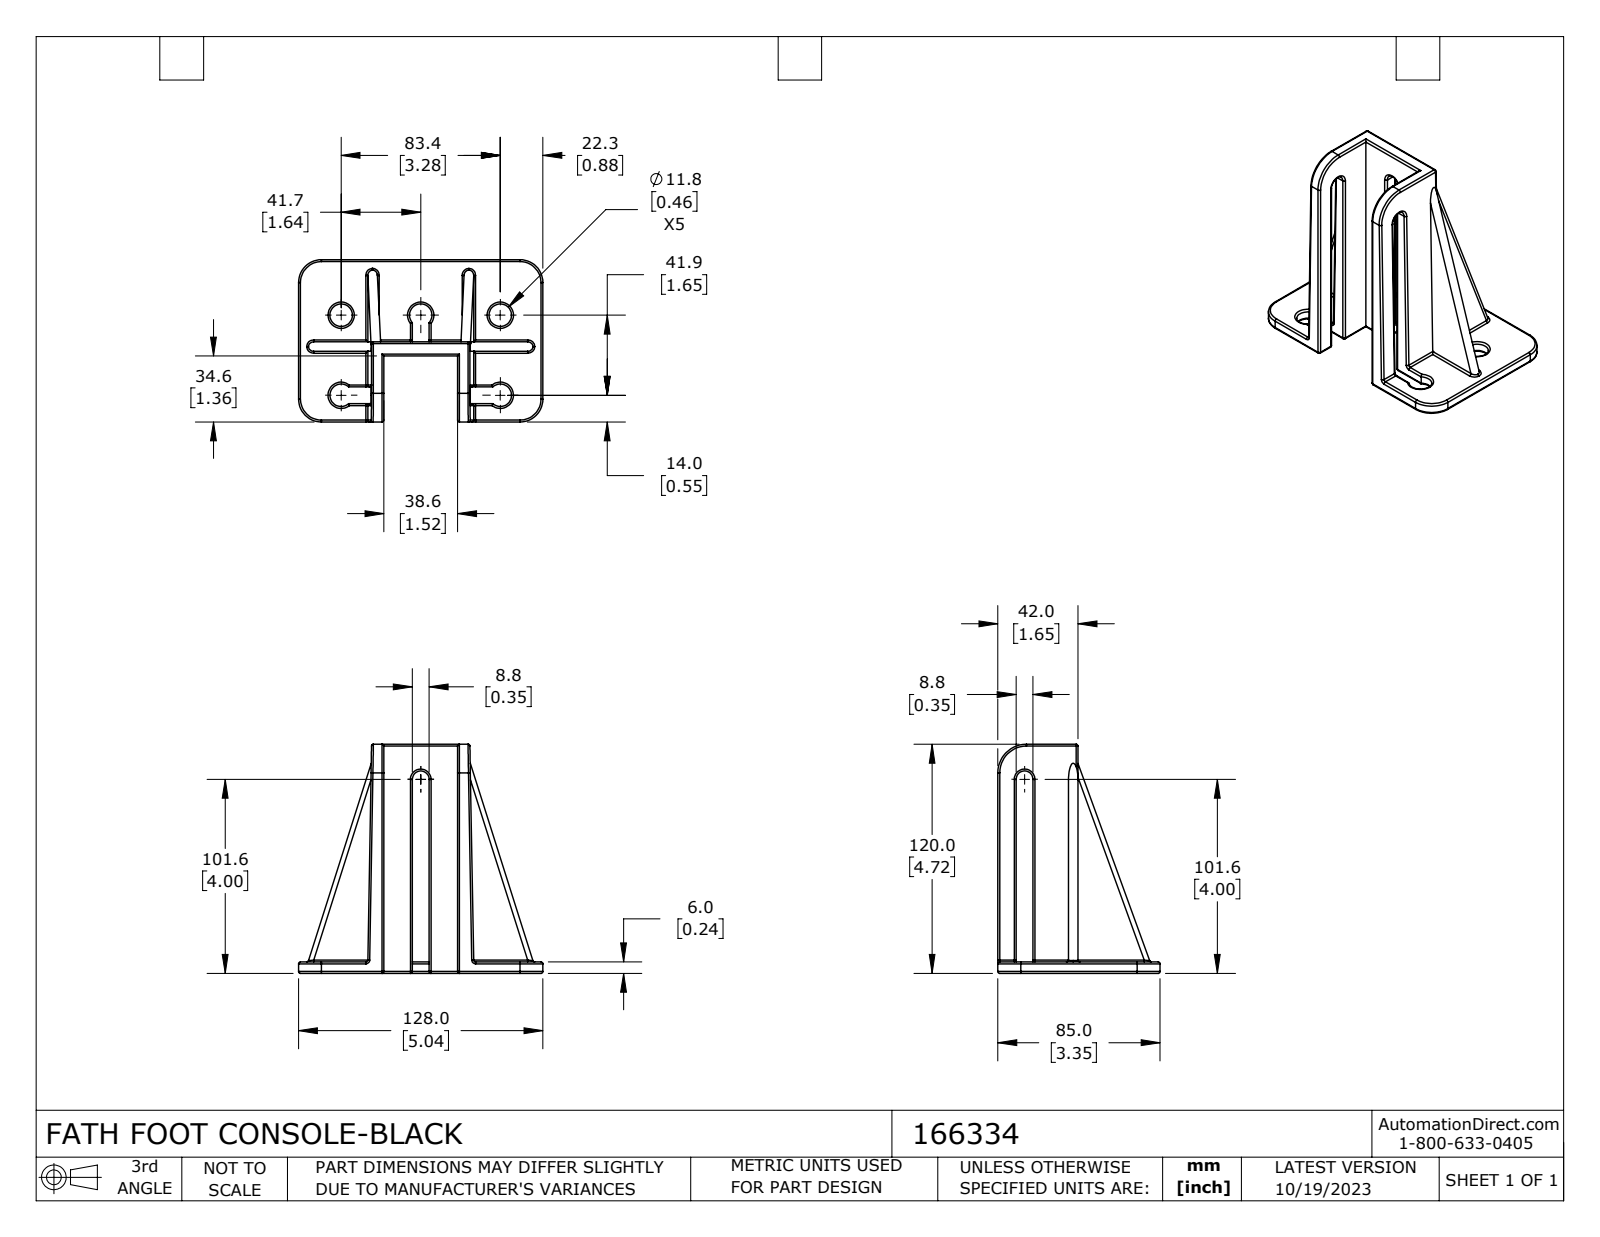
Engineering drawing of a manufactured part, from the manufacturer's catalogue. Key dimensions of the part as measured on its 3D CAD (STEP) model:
Part name (STEP PRODUCT): 166334
STEP written by: SolidWorks 2023 (CONFIG_CONTROL_DESIGN)
Units: inches
Bodies: 1 solid, 187 faces (28 planar, 91 cylindrical, 68 other)
Overall size (bounding box): 5.039 × 4.724 × 3.346
Volume: 10.28 in³ · Surface area: 94.98 in²
Round holes (diameter × count): ⌀0.465 ×2
Partial cylindrical surfaces — rounded edges, fillets, slot ends (radius × count): R0.039 ×49, R0.098 ×4, R0.472 ×4, R0.232 ×3, R0.173 ×2, R0.591 ×1
Main face-to-face distances: 0.236, 0.197, 0.293, 1.52, 0.096, 0.346, 1.36, 1.457, 1.654, 0.378
Hole centre spacings: 3.282
